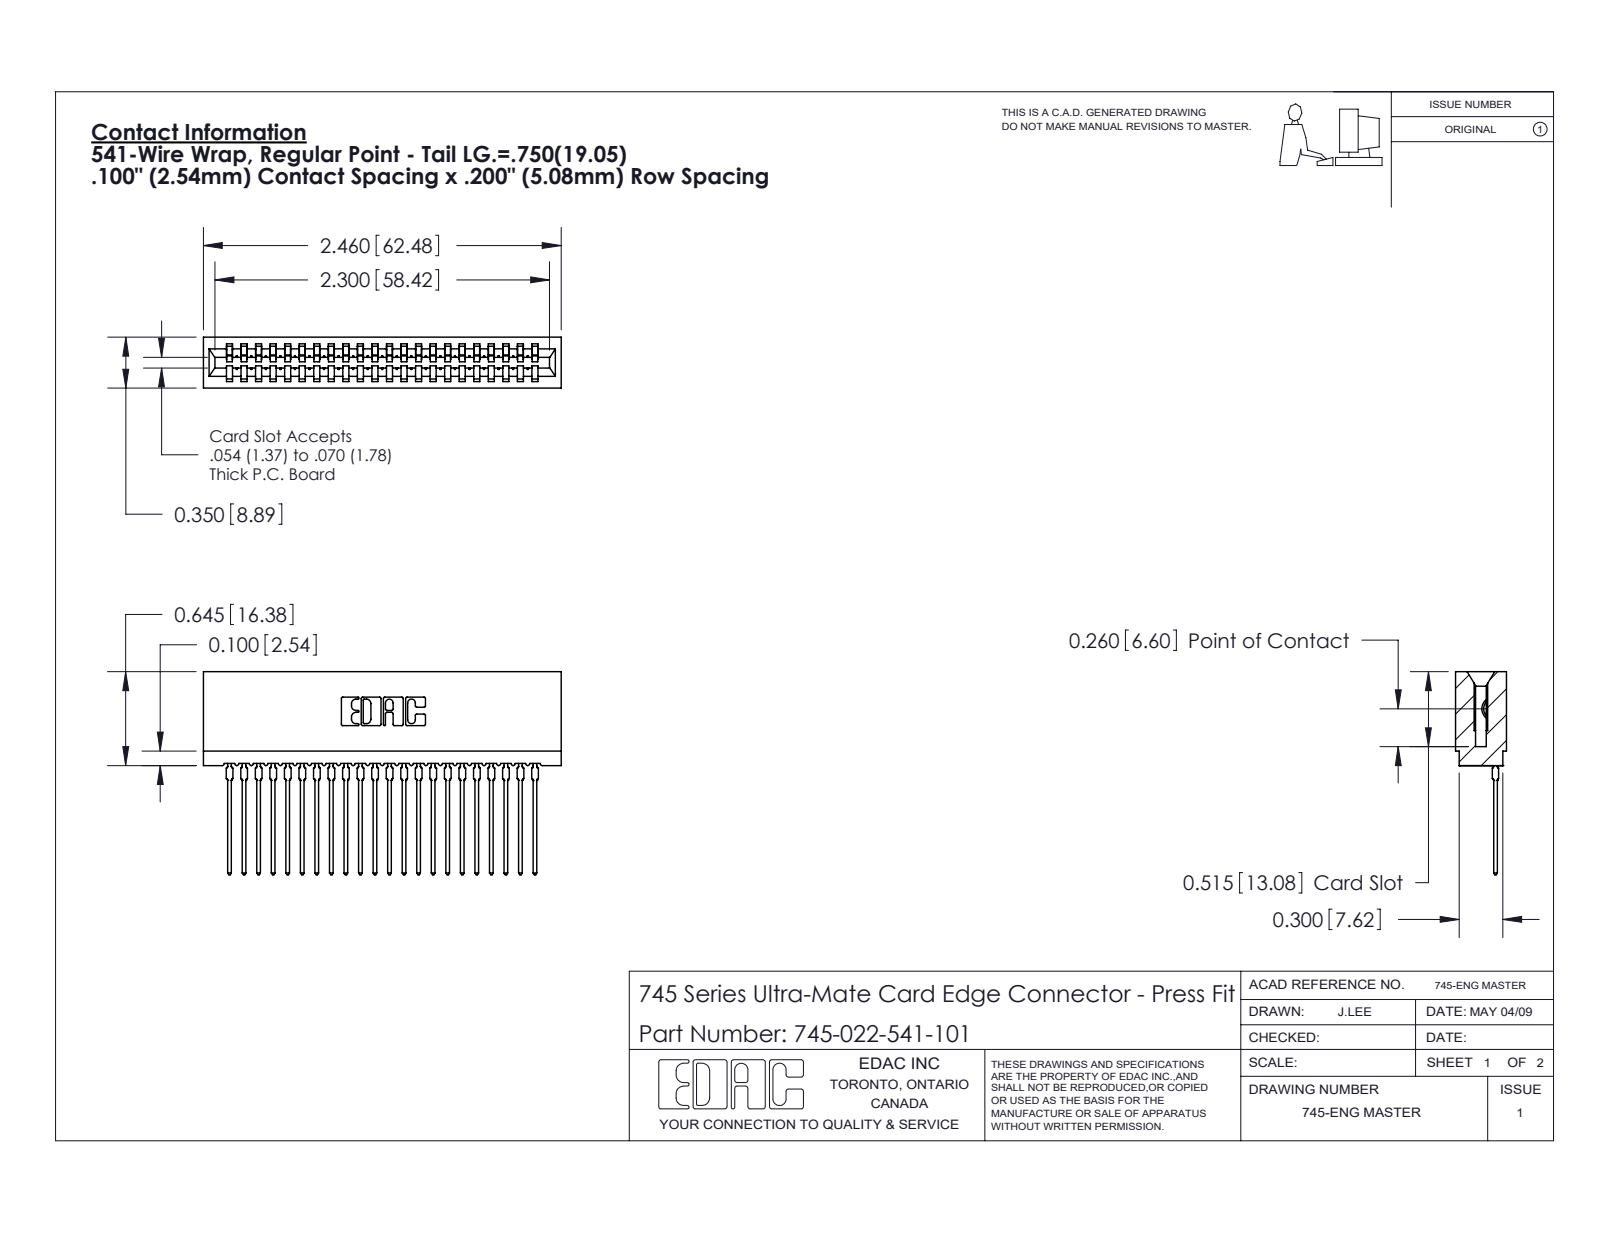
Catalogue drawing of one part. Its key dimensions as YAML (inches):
part_name: "745-292-001_541; 745 Part_Insulator Option - 01; 745-022-541-101"
step_written_by: "SolidWorks 2020 (CONFIG_CONTROL_DESIGN)"
units: inches
bodies: {solids: 23, faces: 2559, planar: 1529, cylindrical: 458, other: 572}
overall_size: [2.46, 1.396, 0.35]
volume: 0.344
surface_area: 16.35
partial_cylinders:
  - {radius: 0.015, count: 44}
  - {radius: 0.021, count: 44}
  - {radius: 0.01, count: 22}
  - {radius: 0.007, count: 6}
  - {radius: 0.031, count: 6}
  - {radius: 0.005, count: 4}
  - {radius: 0.011, count: 4}
  - {radius: 0.026, count: 3}
face_to_face_distances: [0.1, 0.2, 0.35, 0.138, 0.212, 0.063, 0.287, 0.4, 0.3, 0.045]
